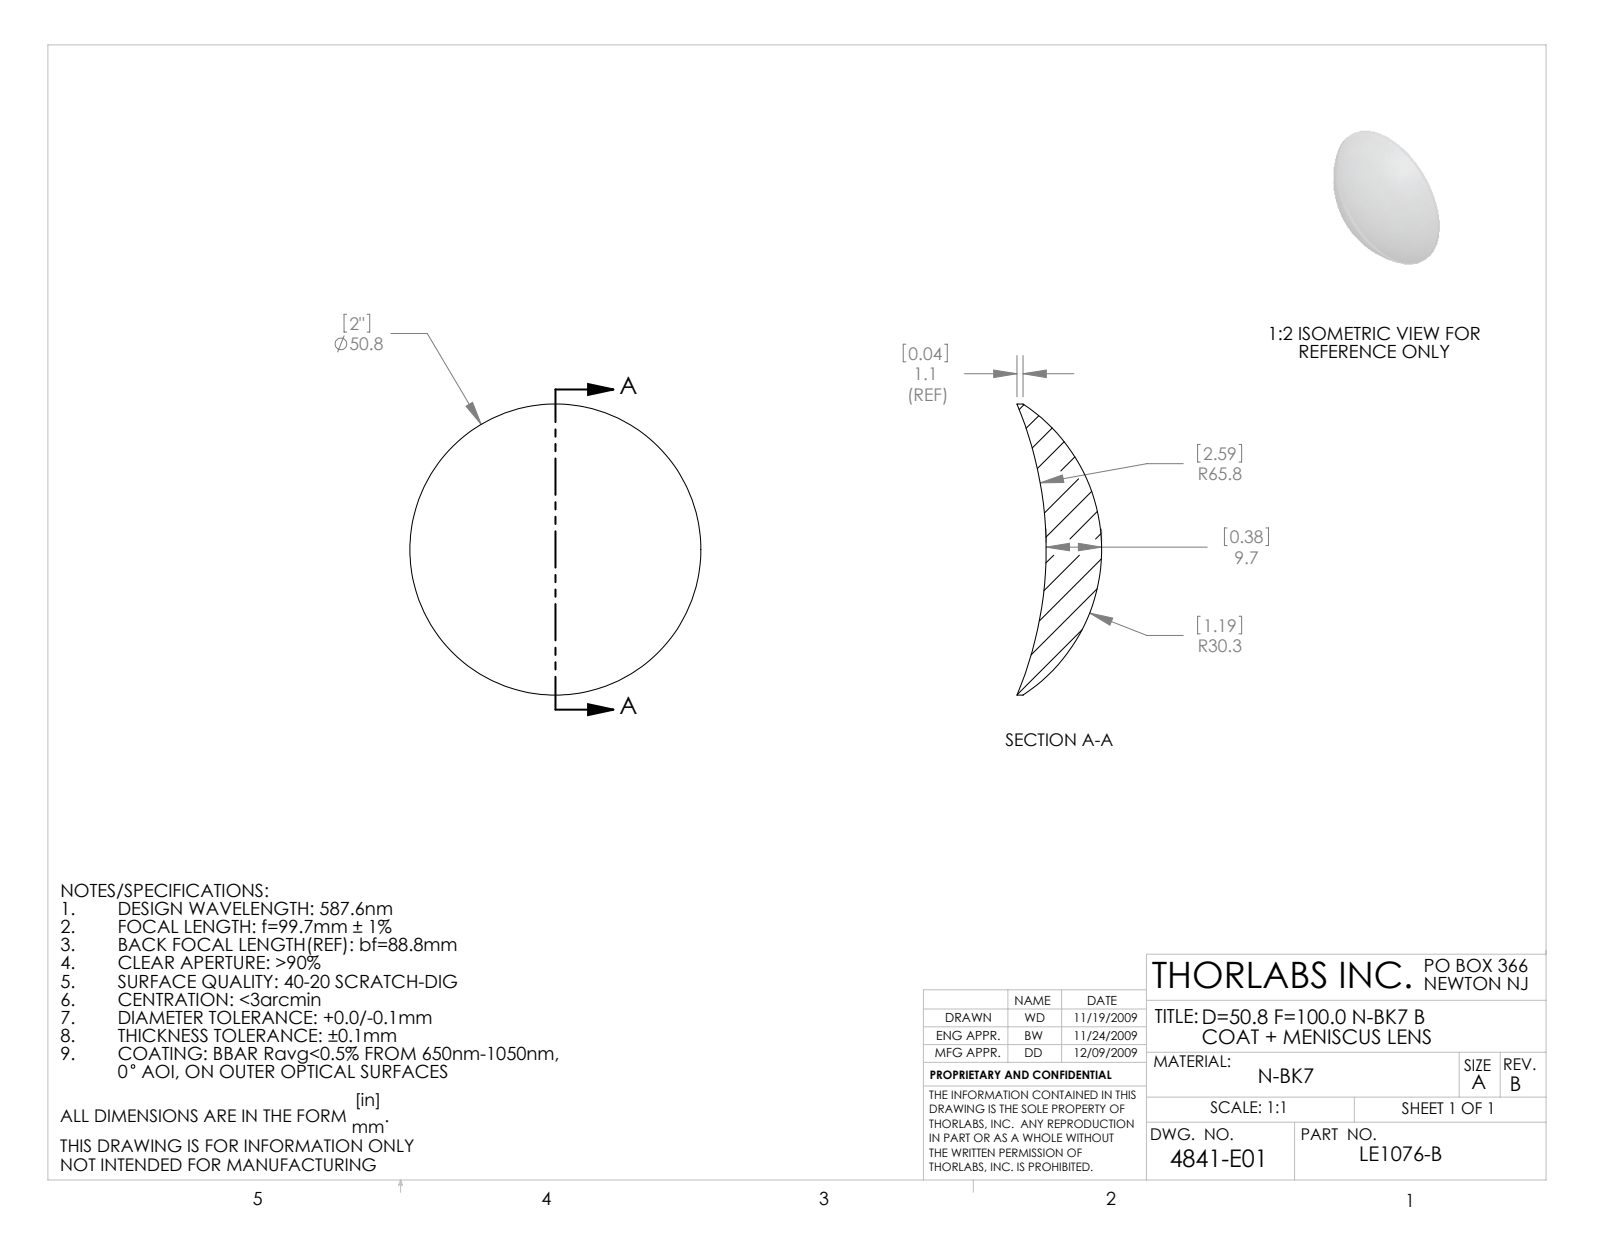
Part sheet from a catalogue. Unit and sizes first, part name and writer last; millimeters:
Units: millimetres
Overall size (bounding box): 50.8 × 50.8 × 14.8
Round bosses / shafts (diameter × count): ⌀50.8 ×1
Volume: 12 189 mm³ · Surface area: 4 897 mm²
Bodies: 1 solid, 6 faces (0 planar, 2 cylindrical, 4 other)
Part name (STEP PRODUCT): 4841-E0W
STEP written by: SolidWorks 2009 (AUTOMOTIVE_DESIGN)
